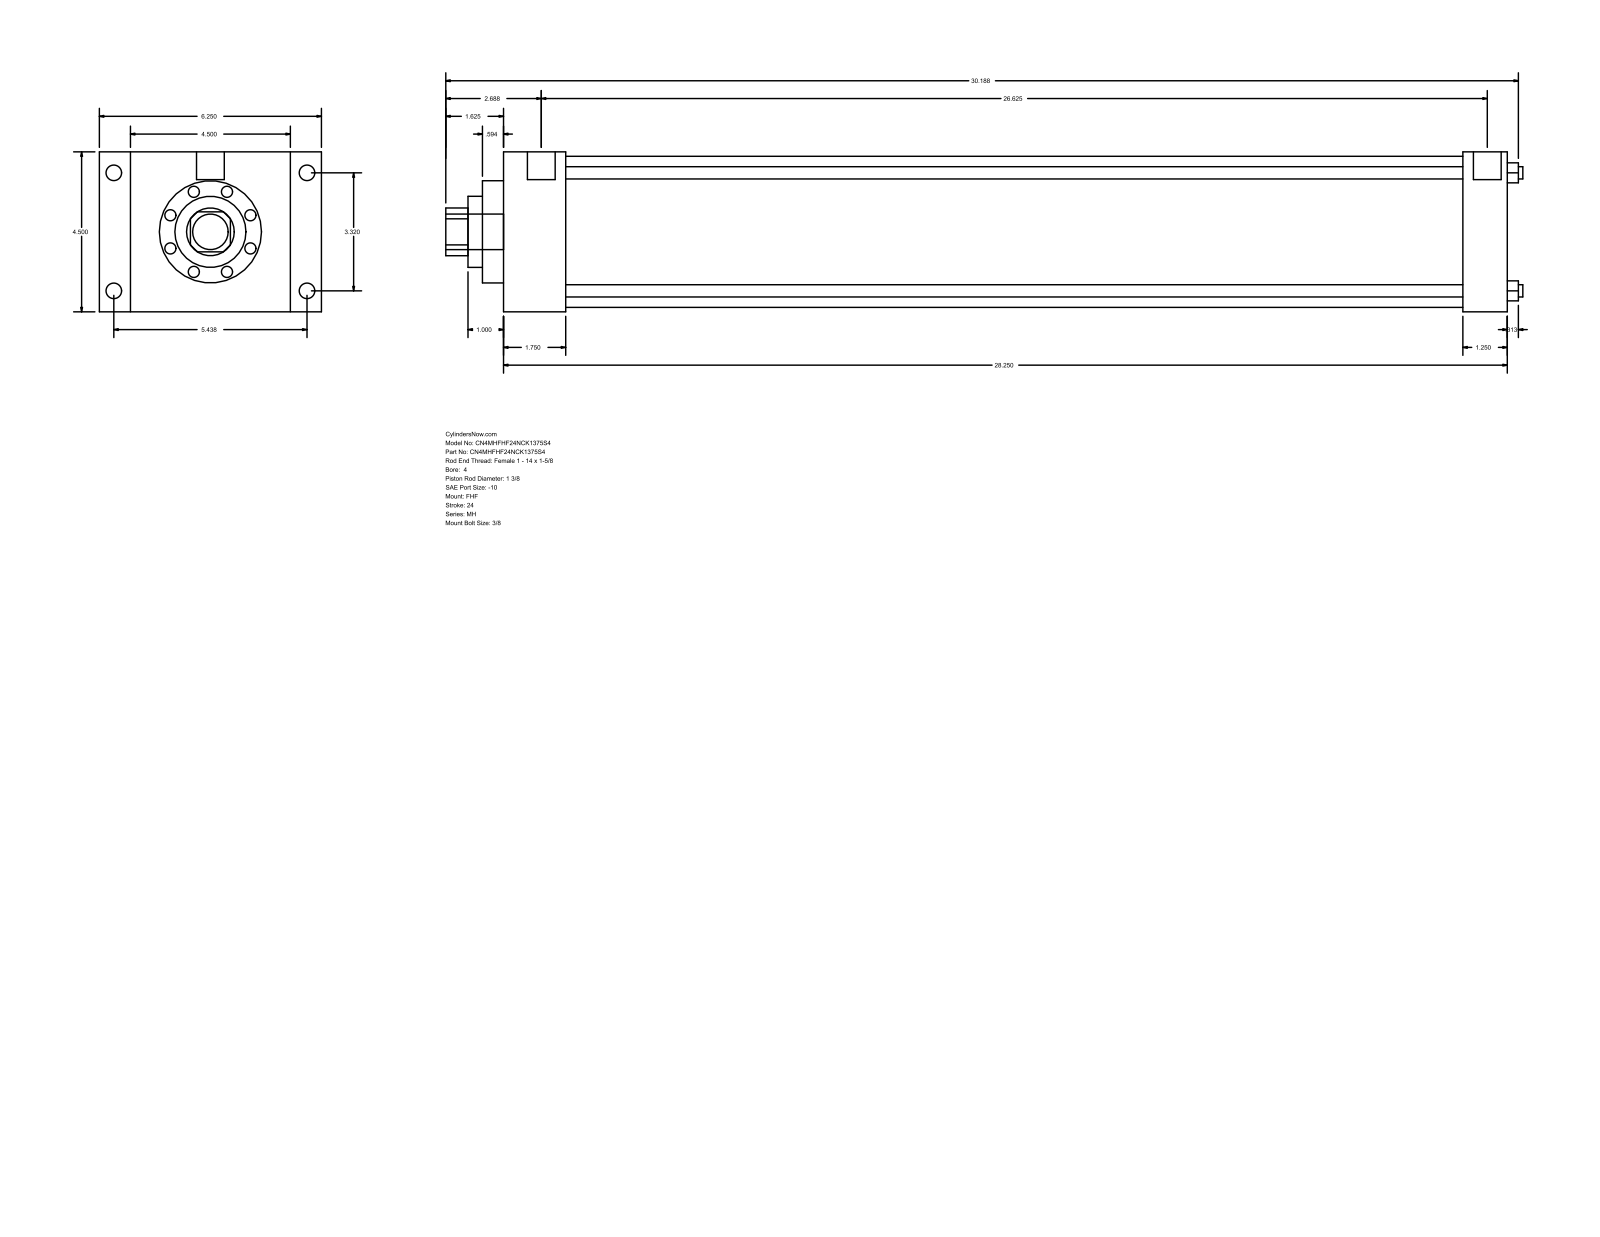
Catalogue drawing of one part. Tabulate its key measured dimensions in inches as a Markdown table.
| quantity | value |
| --- | --- |
| part name | MH_FHF__0400_1.375 |
| STEP written by | GSSL Pune (CONFIG_CONTROL_DESIGN) |
| units | inches |
| bodies | 0 solids, 90 faces (61 planar, 29 cylindrical, 0 other) |
| overall size | 30.313 × 6.25 × 4.5 |
| round holes (diameter × count) | 0.345 × 4, 1.375 × 1, 2 × 1, 2.875 × 1, 4.25 × 1 |
| round bosses / shafts (diameter × count) | 0.438 × 4, 0.344 × 4, 0.781 × 2, 1 × 1 |
| partial cylindrical surfaces (radius × count) | 0.672 × 1 |
| main face-to-face distances | 4.5, 28.25, 1.75, 26.5, 0.875, 5.375, 6.25, 27, 25.25, 1.25 |
| hole center spacings | 2.347, 3.32, 4.695 |
